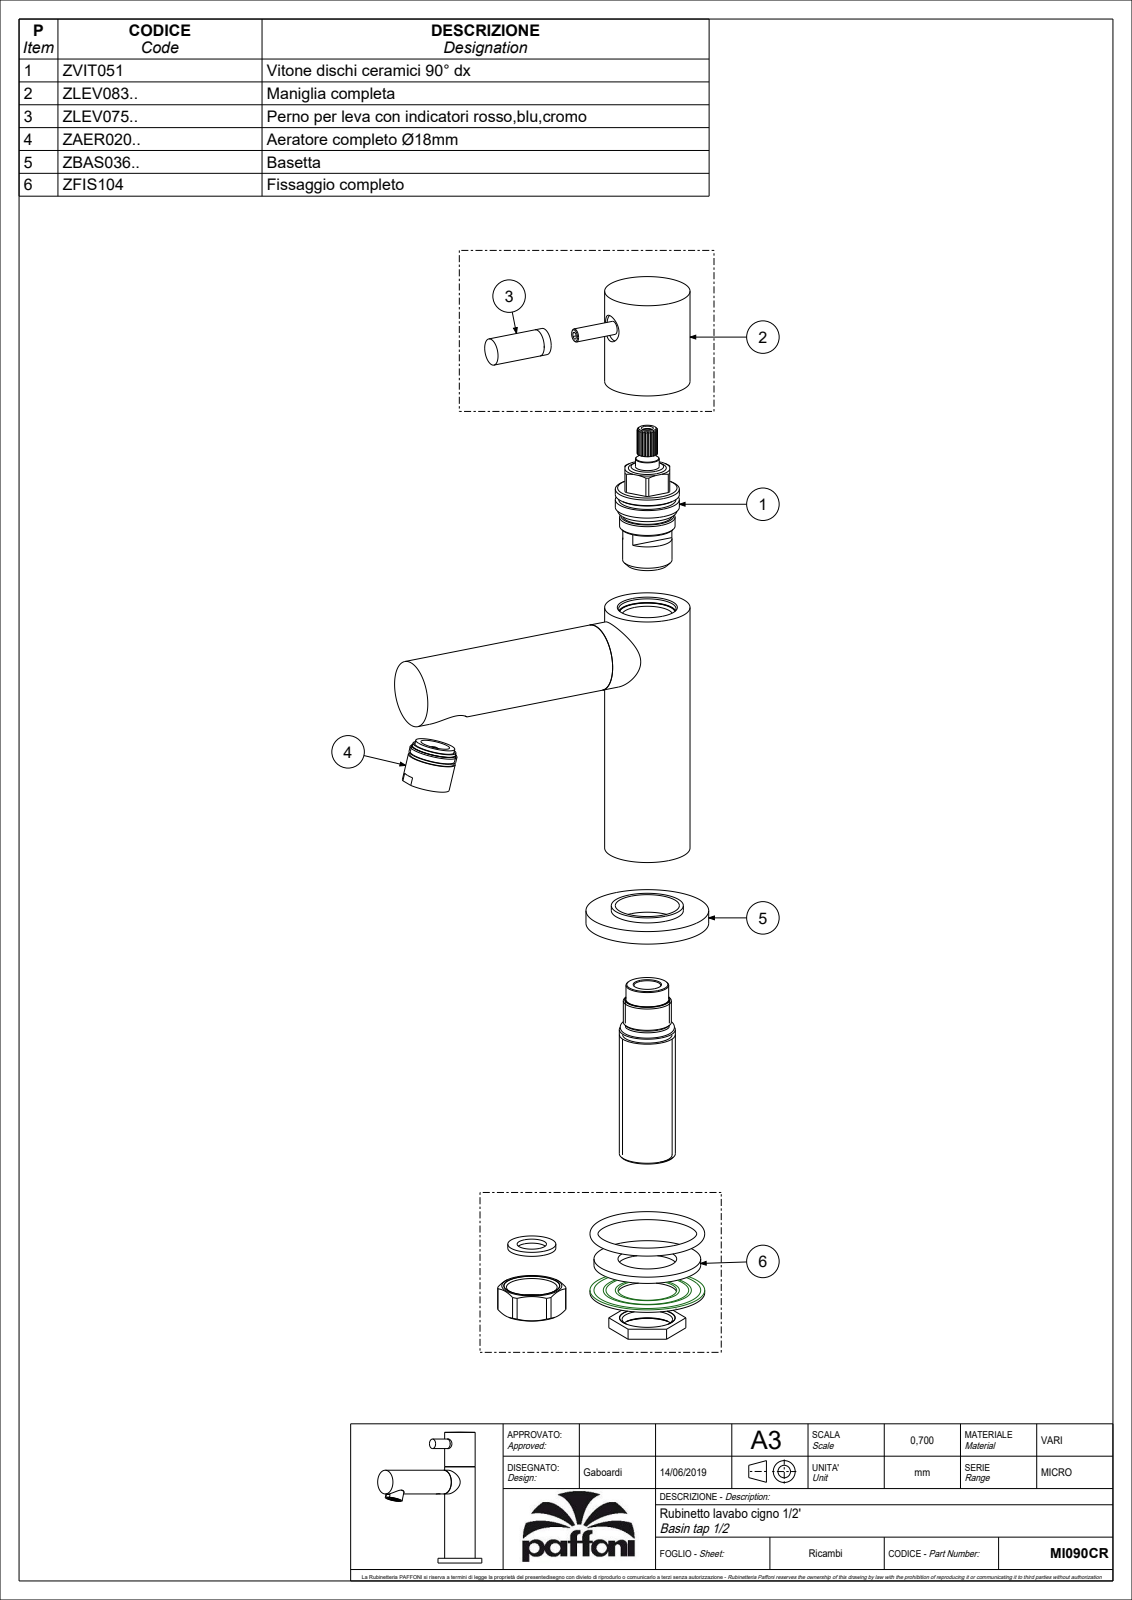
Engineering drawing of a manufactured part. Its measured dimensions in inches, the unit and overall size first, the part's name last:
Units: inches
Overall size (bounding box): 5.413 × 4.938 × 1.811
Round holes (diameter × count): ⌀0.177 ×1, ⌀0.217 ×1, ⌀0.354 ×1, ⌀0.394 ×1, ⌀0.398 ×1, ⌀0.433 ×1, ⌀0.492 ×1, ⌀0.61 ×1, ⌀0.661 ×1, ⌀0.724 ×1, ⌀0.748 ×1, ⌀0.768 ×1
Round bosses / shafts (diameter × count): ⌀1.811 ×1, ⌀1.457 ×1, ⌀1.26 ×1, ⌀1.063 ×1, ⌀0.98 ×1, ⌀0.728 ×1, ⌀0.724 ×1, ⌀0.709 ×1
Partial cylindrical surfaces — rounded edges, fillets, slot ends (radius × count): R0.041 ×1
Main face-to-face distances: 0.197, 0.098, 4.732, 4.535, 0.756, 3.976, 3.78, 3.878, 4.634, 0.295
Hole centre spacings: 1.209
Volume: 8.322 in³ · Surface area: 55.43 in²
Bodies: 1 solid, 194 faces (76 planar, 78 cylindrical, 40 other)
Part name (STEP PRODUCT): MI090CR
STEP written by: CREO PARAMETRIC BY PTC INC, 2020044 (CONFIG_CONTROL_DESIGN)
